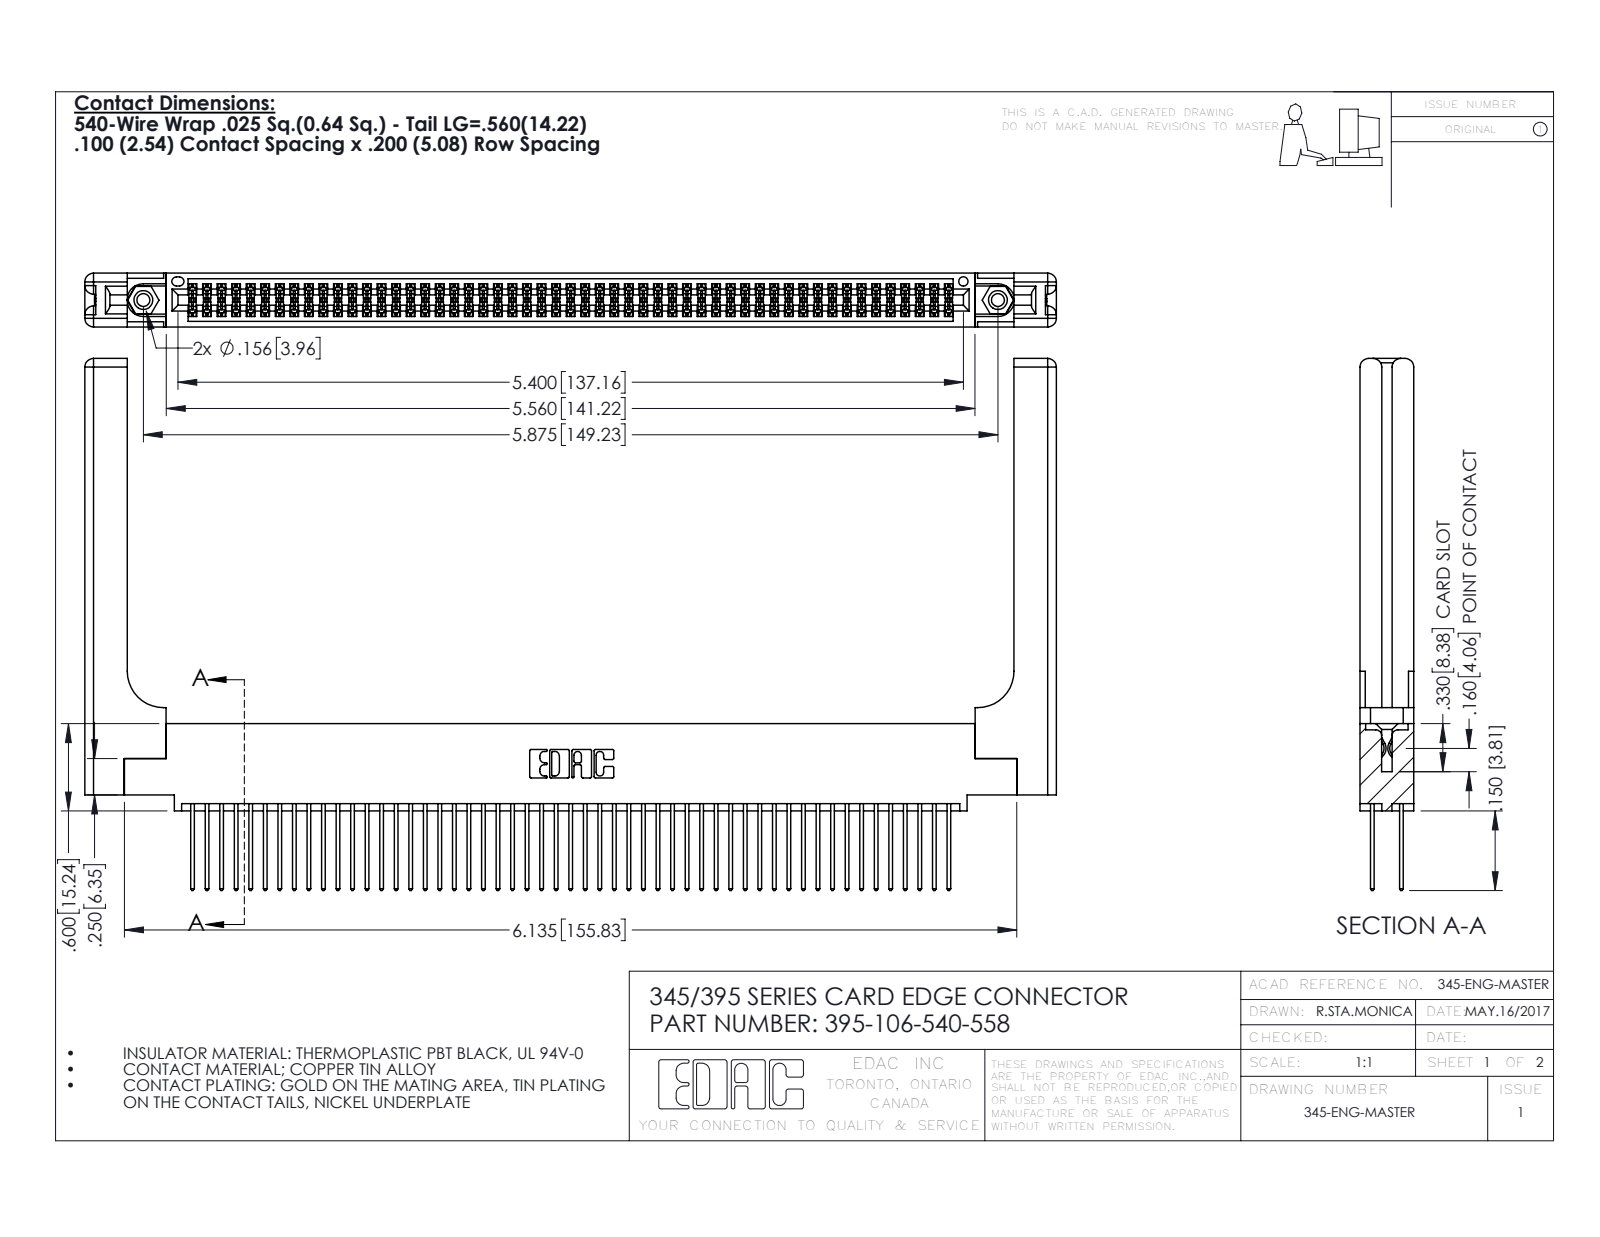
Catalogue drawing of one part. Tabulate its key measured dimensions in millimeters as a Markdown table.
| quantity | value |
| --- | --- |
| part name | 345-292-001_345-293-140; 345-220-058_345-220-058; 345 Part_0.110 Offset - 0.156 Dia-TH; 395-106-540-558 (+1 more) |
| STEP written by | SolidWorks 2016 (CONFIG_CONTROL_DESIGN) |
| units | millimeters |
| bodies | 111 solids, 5686 faces (3730 planar, 1896 cylindrical, 60 other) |
| overall size | 169.6 × 92.9 × 9.4 |
| volume | 25 380 mm³ |
| surface area | 32 230 mm² |
| round holes (diameter × count) | 2.3 × 2, 3.2 × 2, 4 × 2, 1.6 × 1 |
| round bosses / shafts (diameter × count) | 3.9 × 2 |
| partial cylindrical surfaces (radius × count) | 0.2 × 159, 0.3 × 106, 0.3 × 22, 1.5 × 16, 0.2 × 6, 0.8 × 6, 0.7 × 3, 0.4 × 2 |
| main face-to-face distances | 1.8, 7.6, 9.4, 2.5, 6.9, 0.6, 5.1, 5.7, 4.4, 3.8 |
| hole center spacings | 6.9, 143.2, 149.2 |
